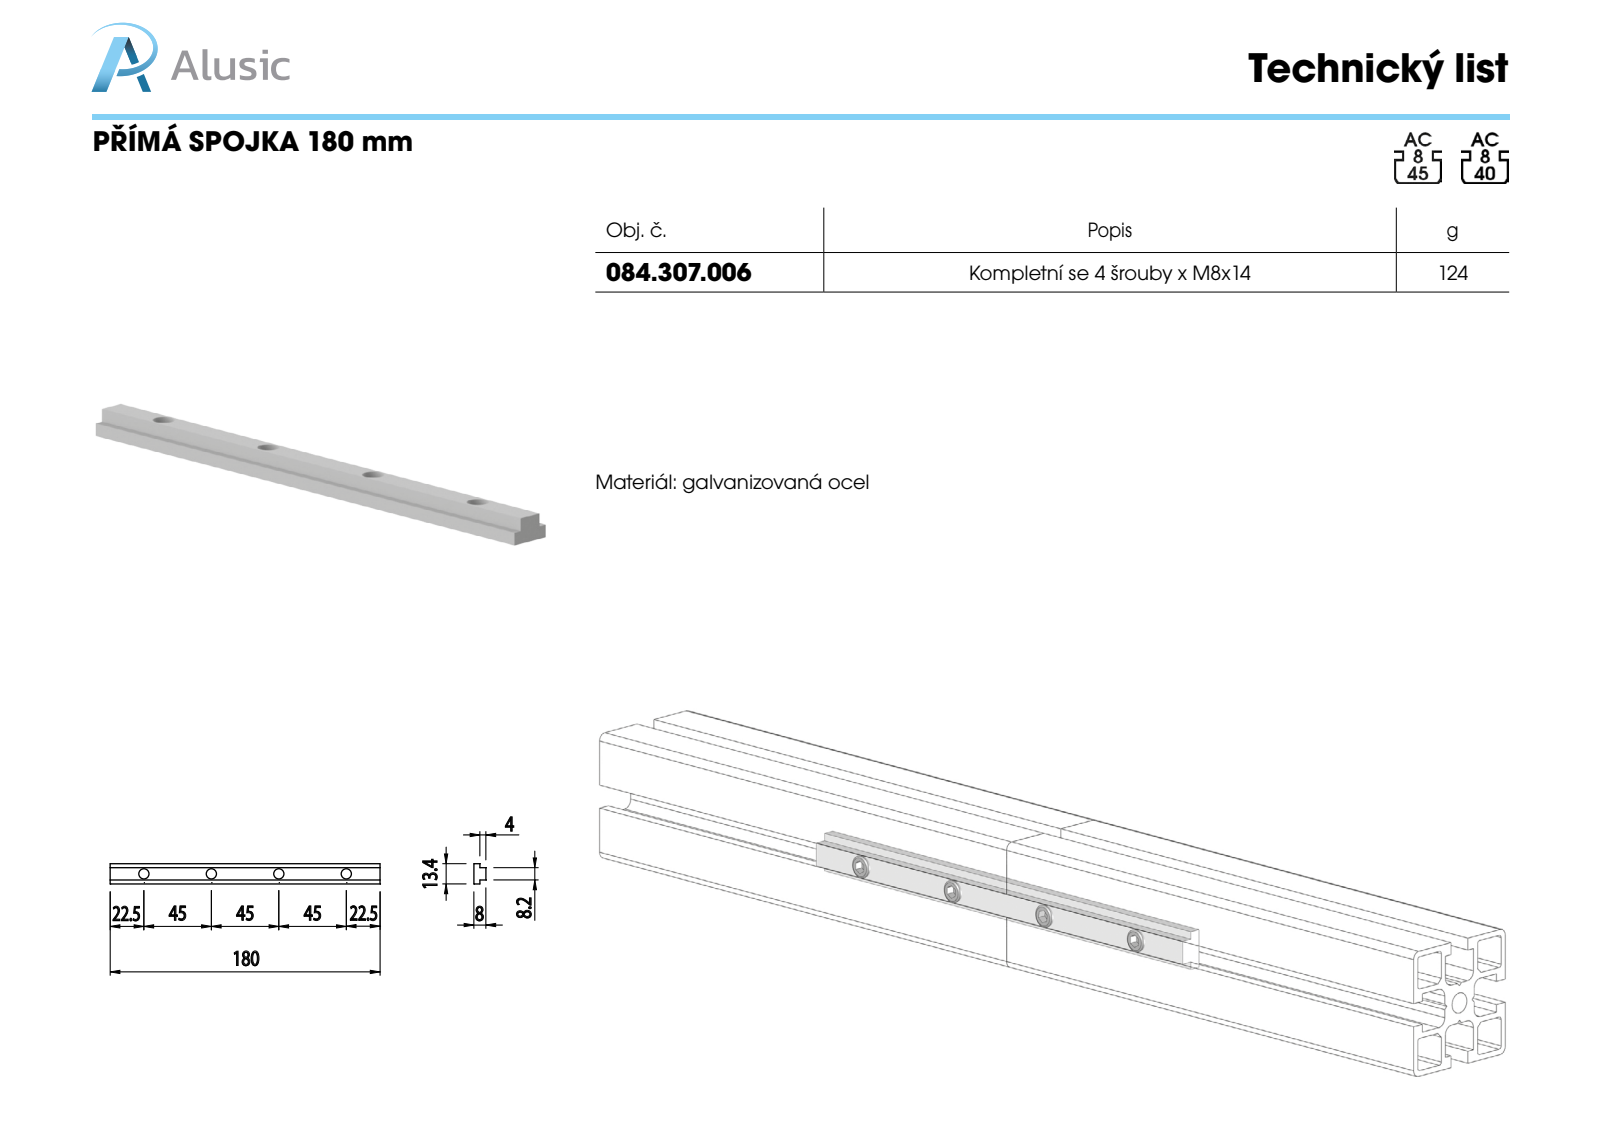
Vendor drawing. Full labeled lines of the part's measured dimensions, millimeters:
Part name (STEP PRODUCT): 084.307.006
STEP written by: SolidWorks 2011 (CONFIG_CONTROL_DESIGN)
Units: millimetres
Bodies: 1 solid, 18 faces (10 planar, 8 cylindrical, 0 other)
Overall size (bounding box): 180 × 13.5 × 8
Volume: 14 462 mm³ · Surface area: 8 307 mm²
Round holes (diameter × count): ⌀6.8 ×4
Main face-to-face distances: 4, 2.65, 10.85, 8, 13.5, 8.2, 180
Hole centre spacings: 45, 90, 135
